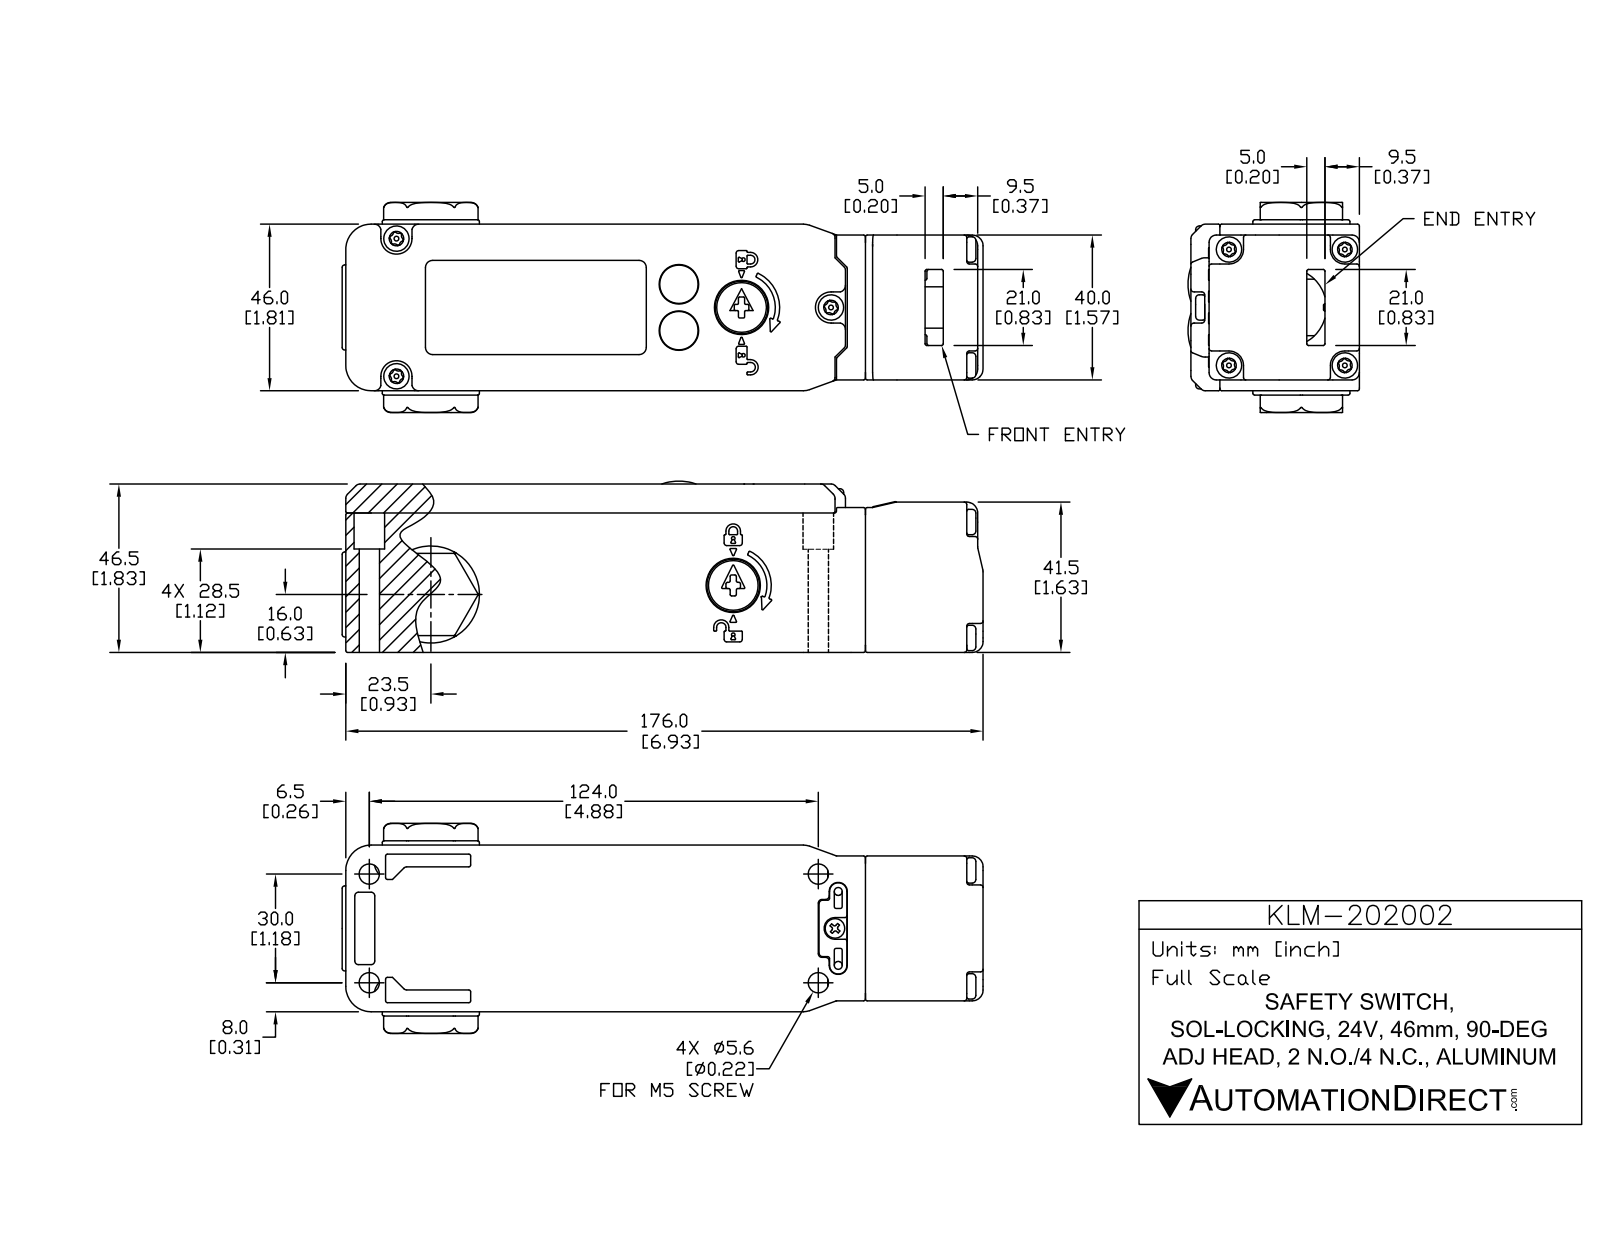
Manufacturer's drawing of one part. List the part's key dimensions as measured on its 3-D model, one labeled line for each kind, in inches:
Part name (STEP PRODUCT): KLM-202002
STEP written by: SolidWorks 2017 (AUTOMOTIVE_DESIGN)
Units: inches
Bodies: 19 solids, 4517 faces (1071 planar, 1803 cylindrical, 1643 other)
Overall size (bounding box): 6.969 × 2.283 × 1.861
Volume: 7.308 in³ · Surface area: 146.4 in²
Round holes (diameter × count): ⌀0.157 ×7, ⌀0.118 ×6, ⌀0.169 ×4, ⌀0.197 ×4, ⌀0.22 ×4, ⌀0.362 ×4, ⌀0.146 ×3, ⌀0.165 ×3, ⌀0.177 ×3, ⌀0.315 ×3, ⌀0.079 ×2, ⌀0.087 ×2
Round bosses / shafts (diameter × count): ⌀0.276 ×7, ⌀0.138 ×7, ⌀0.051 ×7, ⌀0.039 ×4, ⌀0.236 ×3, ⌀0.571 ×2, ⌀0.449 ×2, ⌀0.417 ×2
Partial cylindrical surfaces — rounded edges, fillets, slot ends (radius × count): R0.02 ×519, R0.008 ×139, R0.012 ×115, R0.039 ×111, R0.016 ×70, R0.028 ×42, R0.031 ×36, R0.059 ×25
Main face-to-face distances: 0.091, 1.72, 0.087, 1.811, 0.028, 0.098, 1.602, 0.118, 1.732, 1.646
Hole centre spacings: 0.891, 1.26, 0.139, 0.276, 0.277, 0.287, 0.329, 0.335
